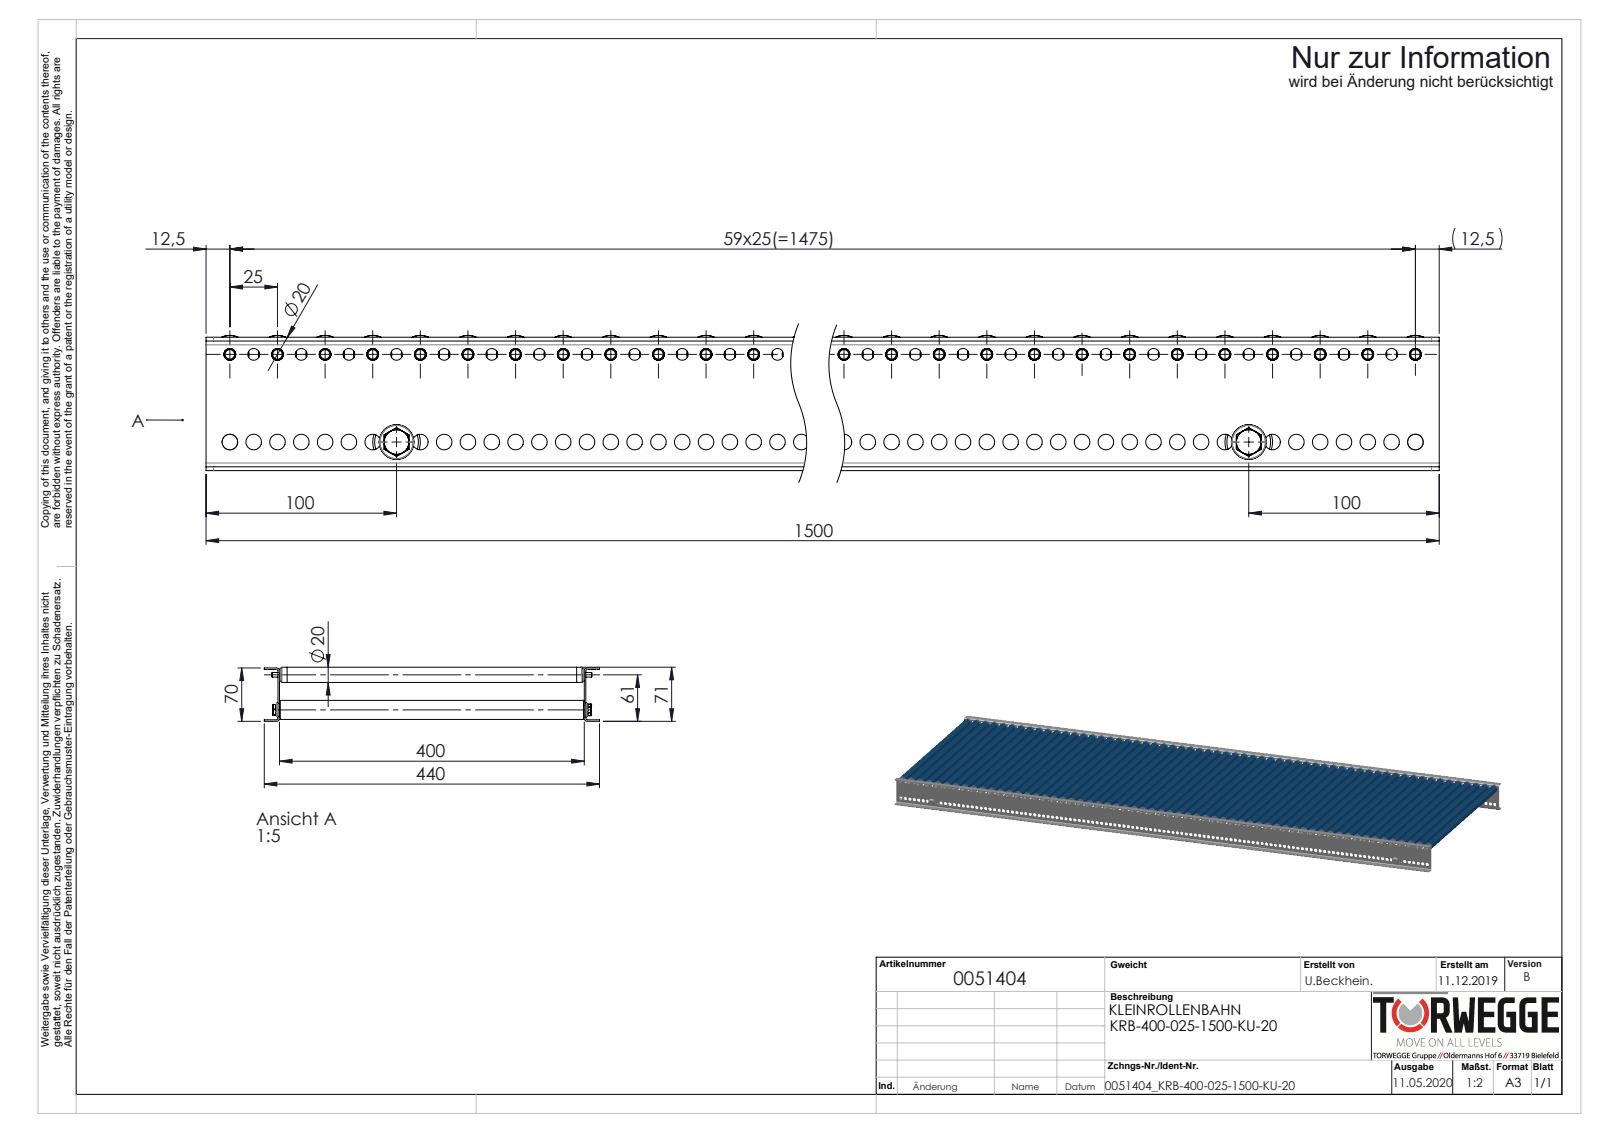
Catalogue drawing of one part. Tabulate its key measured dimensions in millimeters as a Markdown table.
| quantity | value |
| --- | --- |
| part name | 0051404; S100994_Sperrzahnschraube_M08x16-8.8-A2K; 0017012_Tragrollenrohr-Ø20x1,5KU_KFG_L380; 0026257_TYP-KUT50-20X1,5-6 (+4 more) |
| STEP written by | SolidWorks 2020 (AUTOMOTIVE_DESIGN) |
| units | millimeters |
| bodies | 372 solids, 15860 faces (5272 planar, 5916 cylindrical, 4672 other) |
| overall size | 1500 × 440 × 71 |
| volume | 4 101 000 mm³ |
| surface area | 4 345 000 mm² |
| round holes (diameter × count) | 6.2 × 119, 8.2 × 119, 6.1 × 60, 12.4 × 60, 13.2 × 60, 14.6 × 60, 16.2 × 60, 17 × 60, 17.2 × 60, 6.8 × 2 |
| round bosses / shafts (diameter × count) | 20 × 60, 19.9 × 60, 17.1 × 60, 16.8 × 60, 16.5 × 60, 11.4 × 60, 11.1 × 60, 10.2 × 60 |
| partial cylindrical surfaces (radius × count) | 4.05 × 60, 4 × 8, 2 × 4 |
| main face-to-face distances | 2, 402, 68, 400, 404, 70, 66, 392, 10, 12 |
| hole center spacings | 12.5, 25, 37.5, 50, 62.5, 75, 87.5, 100 |
